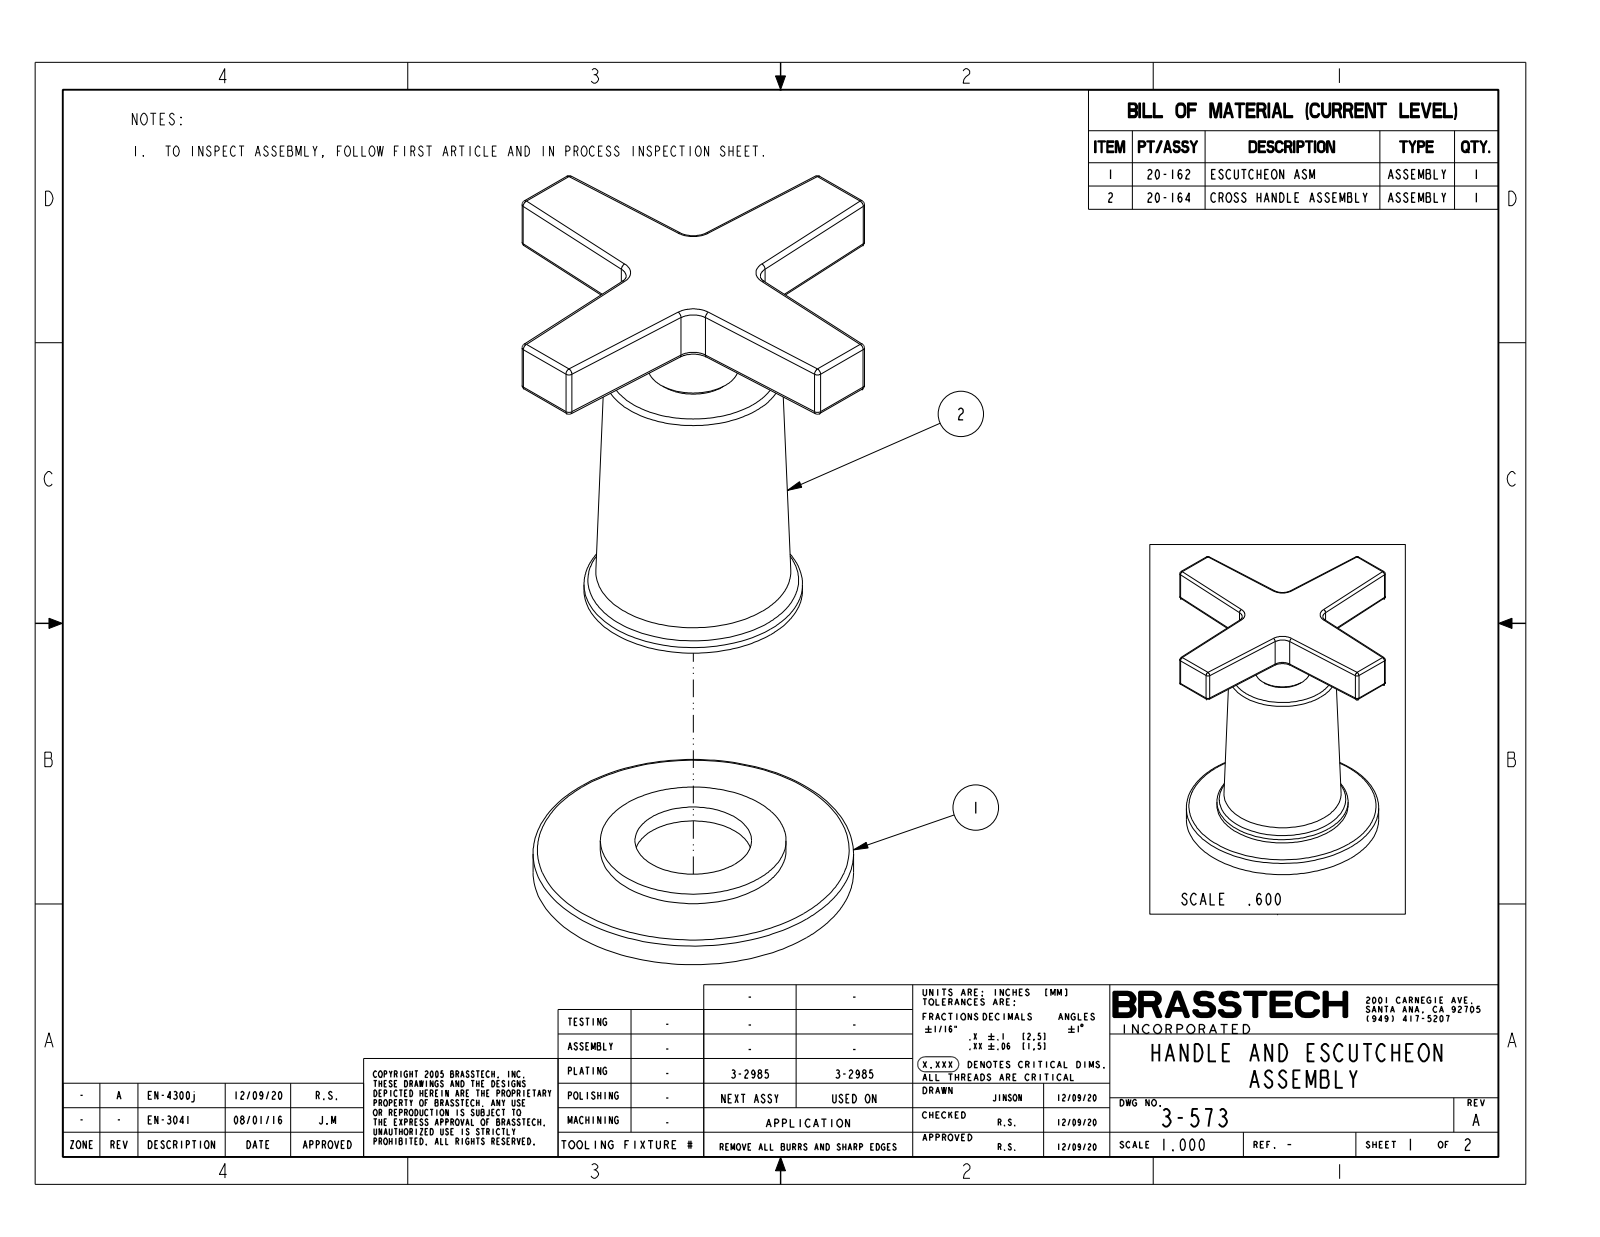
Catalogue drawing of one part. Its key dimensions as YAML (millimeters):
part_name: "3-573"
step_written_by: "CREO PARAMETRIC BY PTC INC, 2018400 (CONFIG_CONTROL_DESIGN)"
units: millimeters
bodies: {solids: 1, faces: 101, planar: 19, cylindrical: 46, other: 36}
overall_size: [73.3, 73.3, 72.9]
volume: 71020
surface_area: 17170
round_bosses_or_shafts:
  - {diameter: 55.9, count: 1}
  - {diameter: 38.1, count: 1}
  - {diameter: 32.4, count: 1}
  - {diameter: 15.9, count: 1}
  - {diameter: 13.3, count: 1}
partial_cylinders:
  - {radius: 0.8, count: 32}
  - {radius: 3.2, count: 4}
face_to_face_distances: [72.9, 4.7, 68.1, 63.4, 58.6, 9.5, 52, 47.2, 11.4, 20.9]
